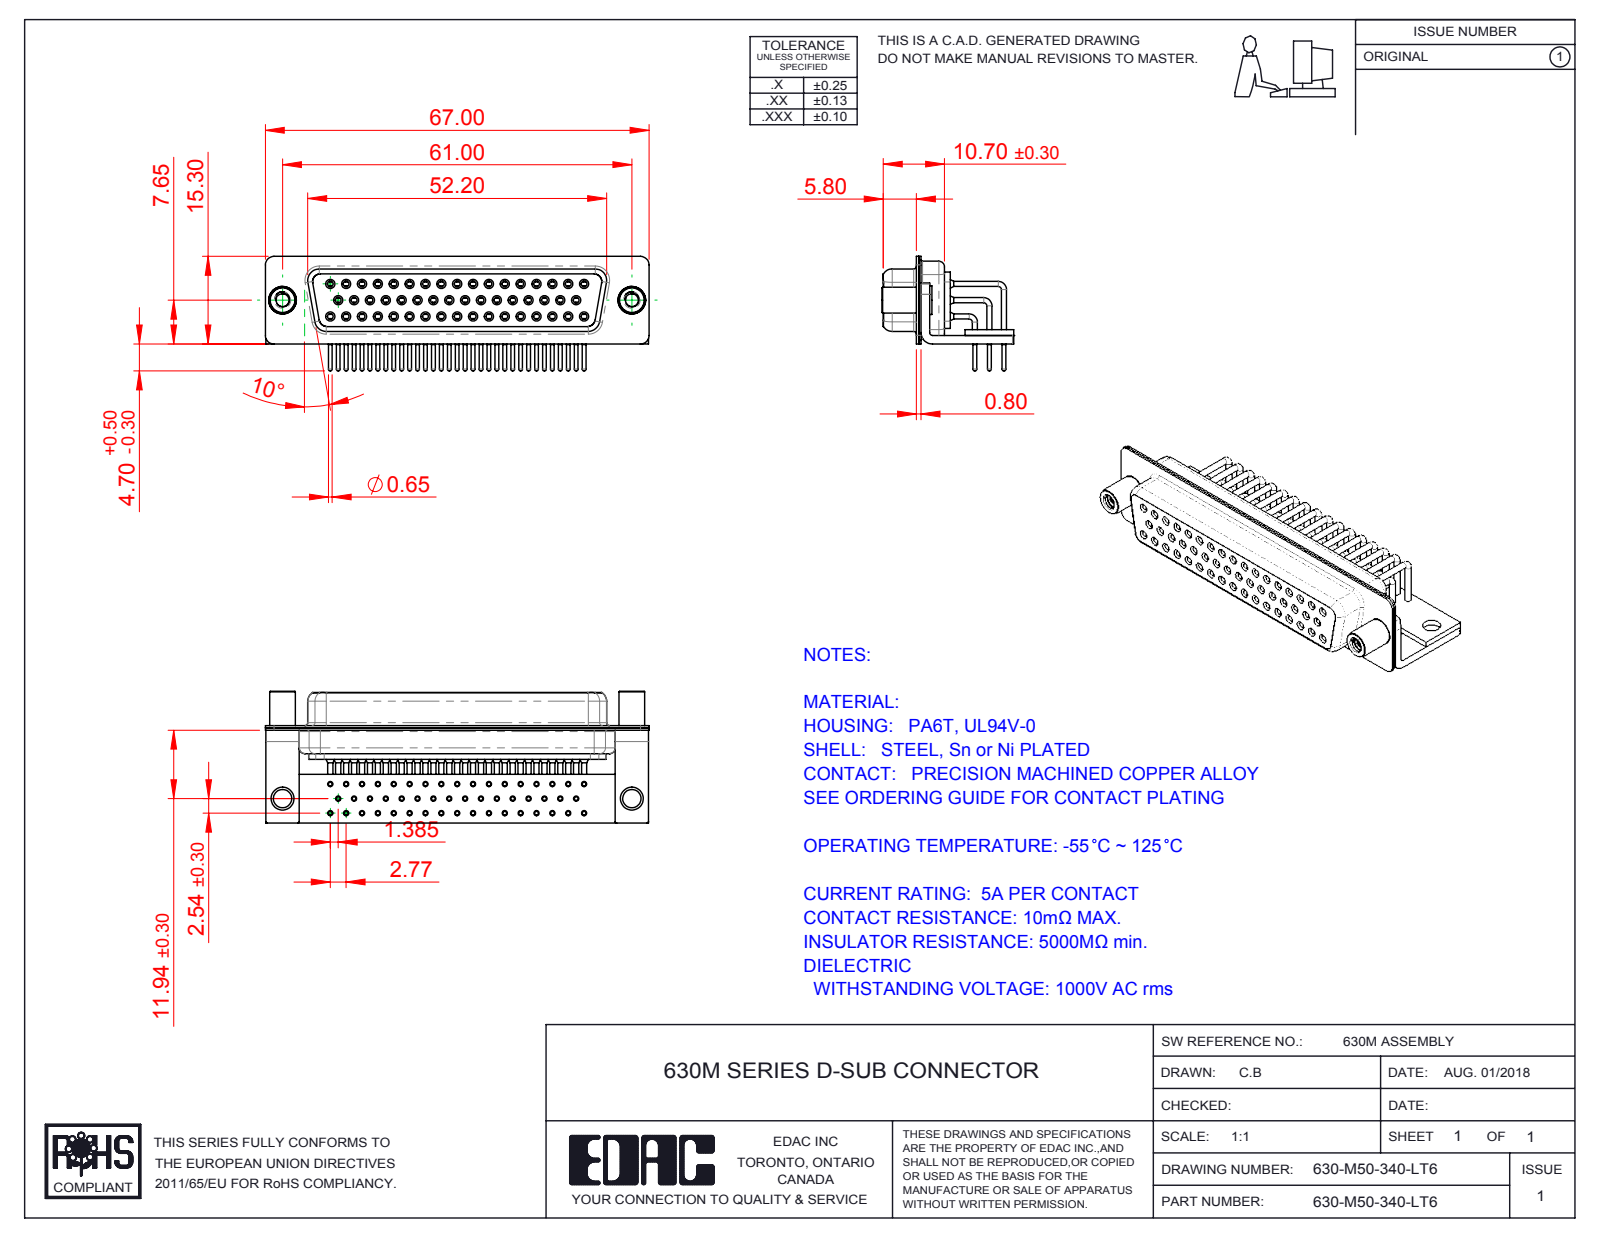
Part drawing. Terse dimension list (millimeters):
name: 630-M50-340-LT6; 630M Housing_50 Contacts; 630M Shell Front_50 Contacts; 630M Contact Row 1_50 Contacts (+6 more)
written by: SolidWorks 2016 (CONFIG_CONTROL_DESIGN)
unit: mm
bodies: 58 solids, 3129 faces (845 planar, 1451 cylindrical, 833 other)
size: 67 × 23 × 20
volume: 7 991 mm³; area: 18 922 mm²
holes: 50× ⌀0.9, 50× ⌀1, 50× ⌀1.1, 50× ⌀1.7, 50× ⌀1.8, 50× ⌀2, 2× ⌀2.26, 2× ⌀3.2, 2× ⌀4, 2× ⌀4.8
bosses: 59× ⌀0.9, 50× ⌀1.6, 50× ⌀1.5, 50× ⌀0.65, 2× ⌀5, 2× ⌀4.9, 2× ⌀4.5
rounds: 16× R0.25, 16× R1.5, 13× R2, 8× R1.35, 8× R1.6, 5× R0.5, 4× R0.6, 4× R0.65
face distances: 0.4, 1, 2.2, 0.85, 1.35, 11.85, 12.25, 5.8, 0.8, 5.9
hole spacings: 2.77, 5.54, 8.31, 11.08, 13.85, 16.62, 3.16, 19.39
